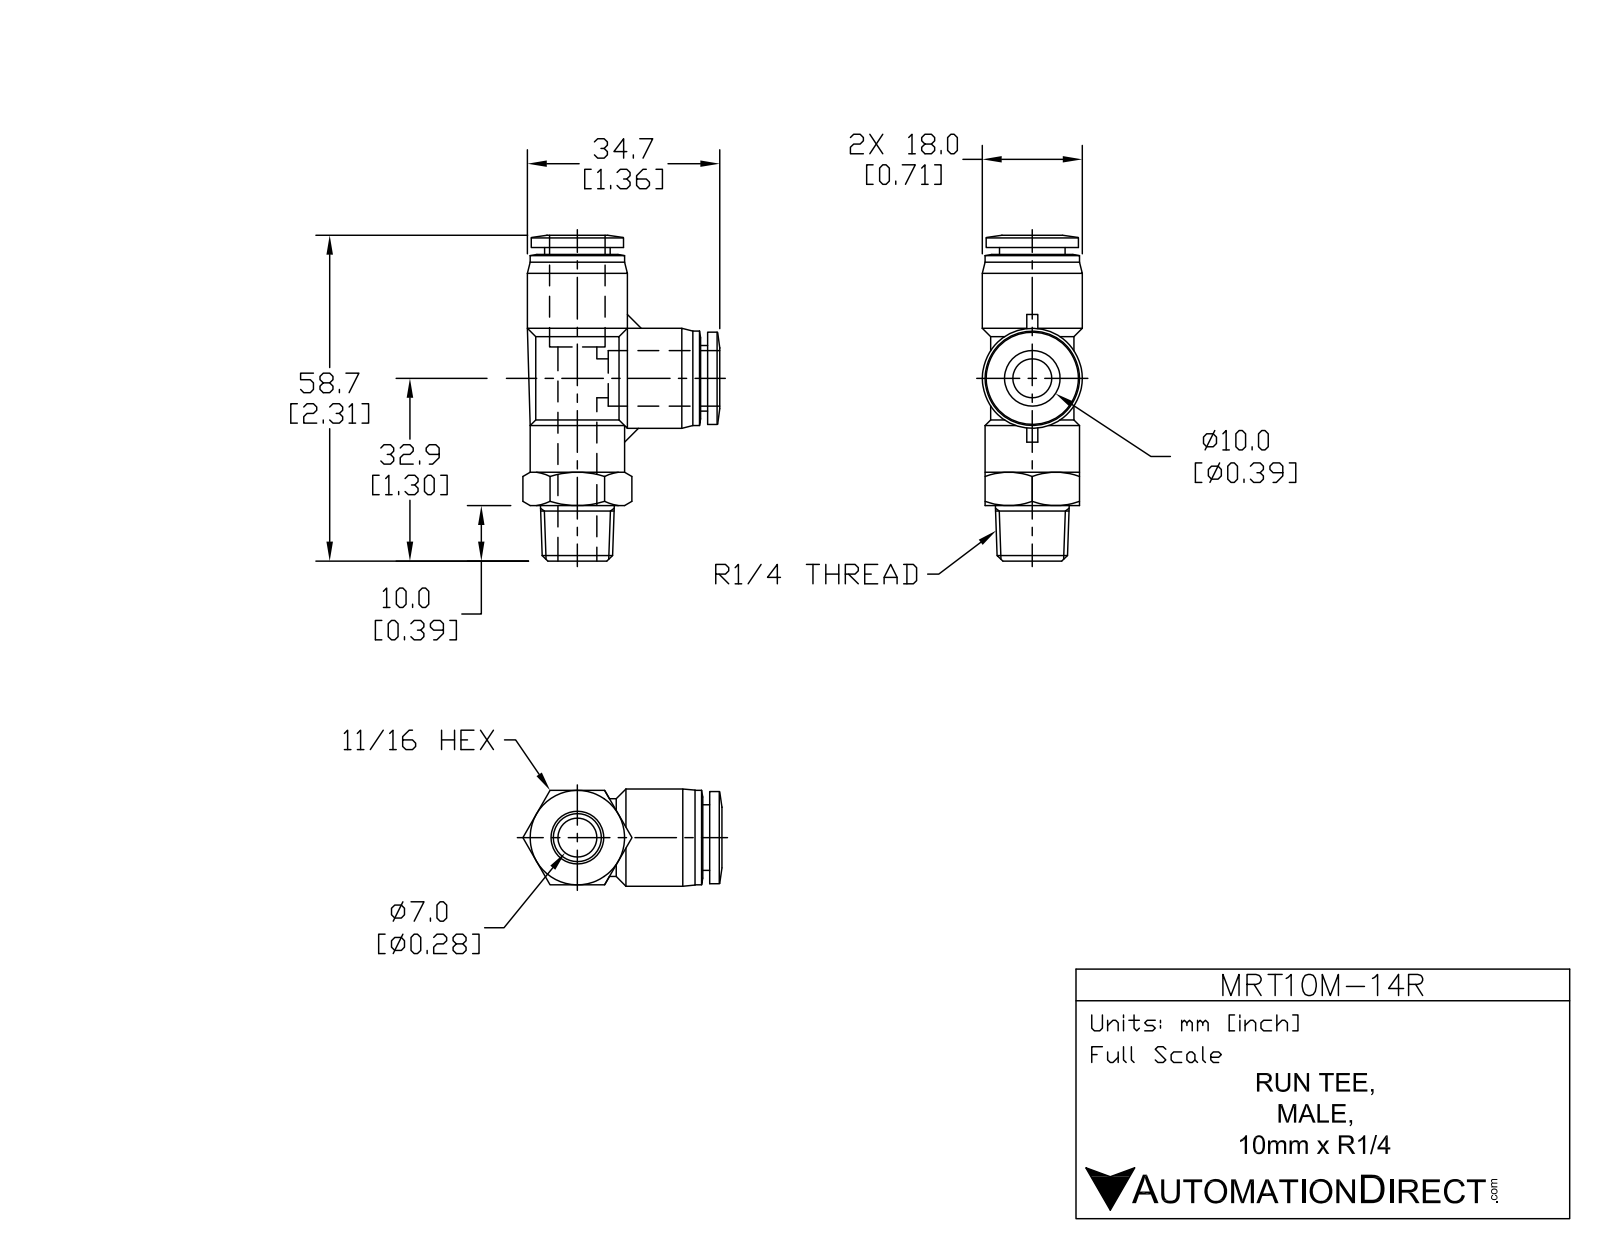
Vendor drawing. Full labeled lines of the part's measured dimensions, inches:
Part name (STEP PRODUCT): MRT10M-14R
STEP written by: SolidWorks 2015 (AUTOMOTIVE_DESIGN)
Units: inches
Bodies: 1 solid, 103 faces (24 planar, 32 cylindrical, 47 other)
Overall size (bounding box): 2.313 × 1.4 × 0.709
Volume: 0.663 in³ · Surface area: 11.05 in²
Round holes (diameter × count): ⌀0.315 ×2, ⌀0.406 ×2
Round bosses / shafts (diameter × count): ⌀0.709 ×2, ⌀0.669 ×2, ⌀0.654 ×2, ⌀0.591 ×2, ⌀0.465 ×2
Main face-to-face distances: 0.669, 0.049, 1.833, 0.659, 0.709, 1.783, 0.295, 0.374, 0.394, 2.177
